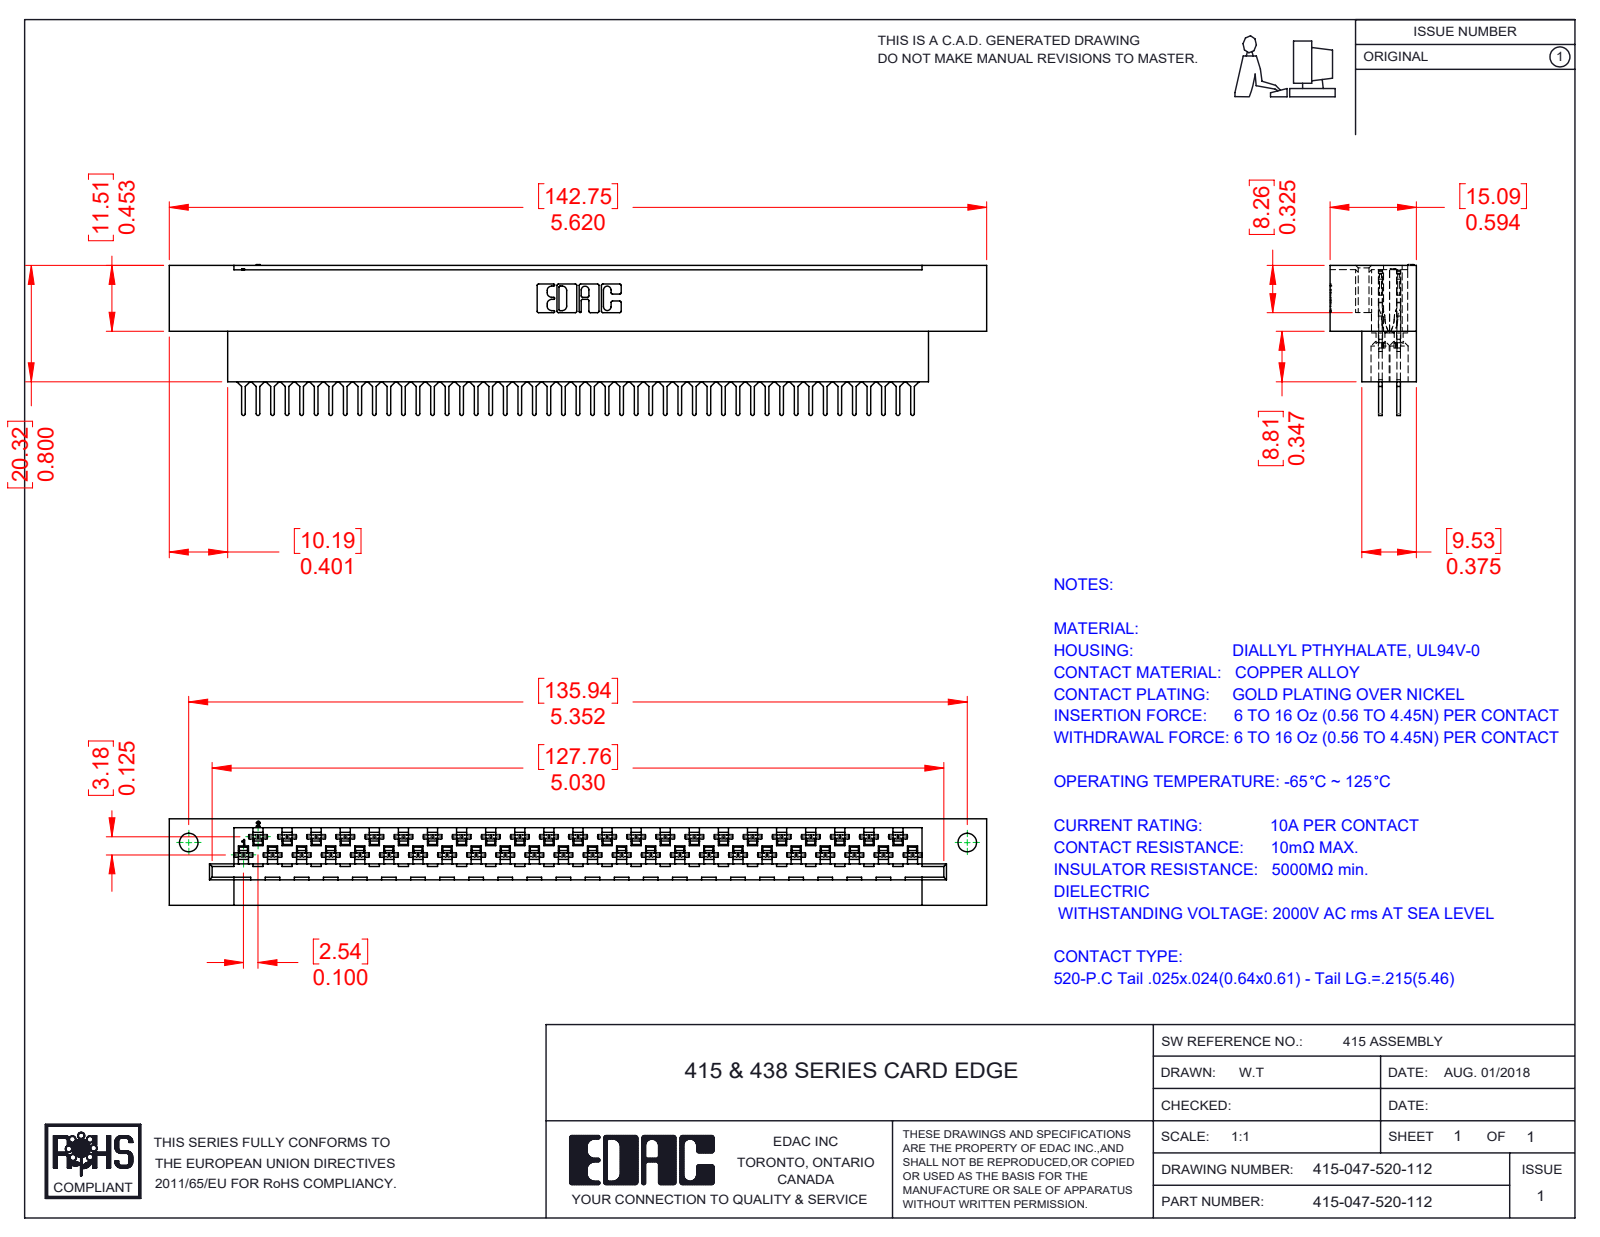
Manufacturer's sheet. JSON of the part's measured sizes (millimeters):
{"part_name": "415-047-520-112; 516-290-001_520; 415-210-001_415-210-047-112", "step_written_by": "SolidWorks 2016 (CONFIG_CONTROL_DESIGN)", "units": "millimeters", "bodies": {"solids": 48, "faces": 4750, "planar": 3039, "cylindrical": 1266, "other": 445}, "overall_size": [142.75, 26.32, 15.09], "volume_mm3": 26509, "surface_area_mm2": 30058, "round_holes": [[1.27, 47], [3.3, 47], [3.25, 2]], "partial_cylinders_radius": [[0.3, 188], [0.56, 188], [0.18, 94], [0.2, 94], [0.41, 94], [2.03, 94], [0.32, 47], [0.25, 22]], "face_to_face_distances": [3.18, 0.61, 1.88, 1.27, 15.09, 1.94, 0.67, 6.61, 8.48, 6], "hole_center_spacings": [5.08, 10.16, 15.24, 20.32, 25.4, 30.48, 35.56, 2.54]}
